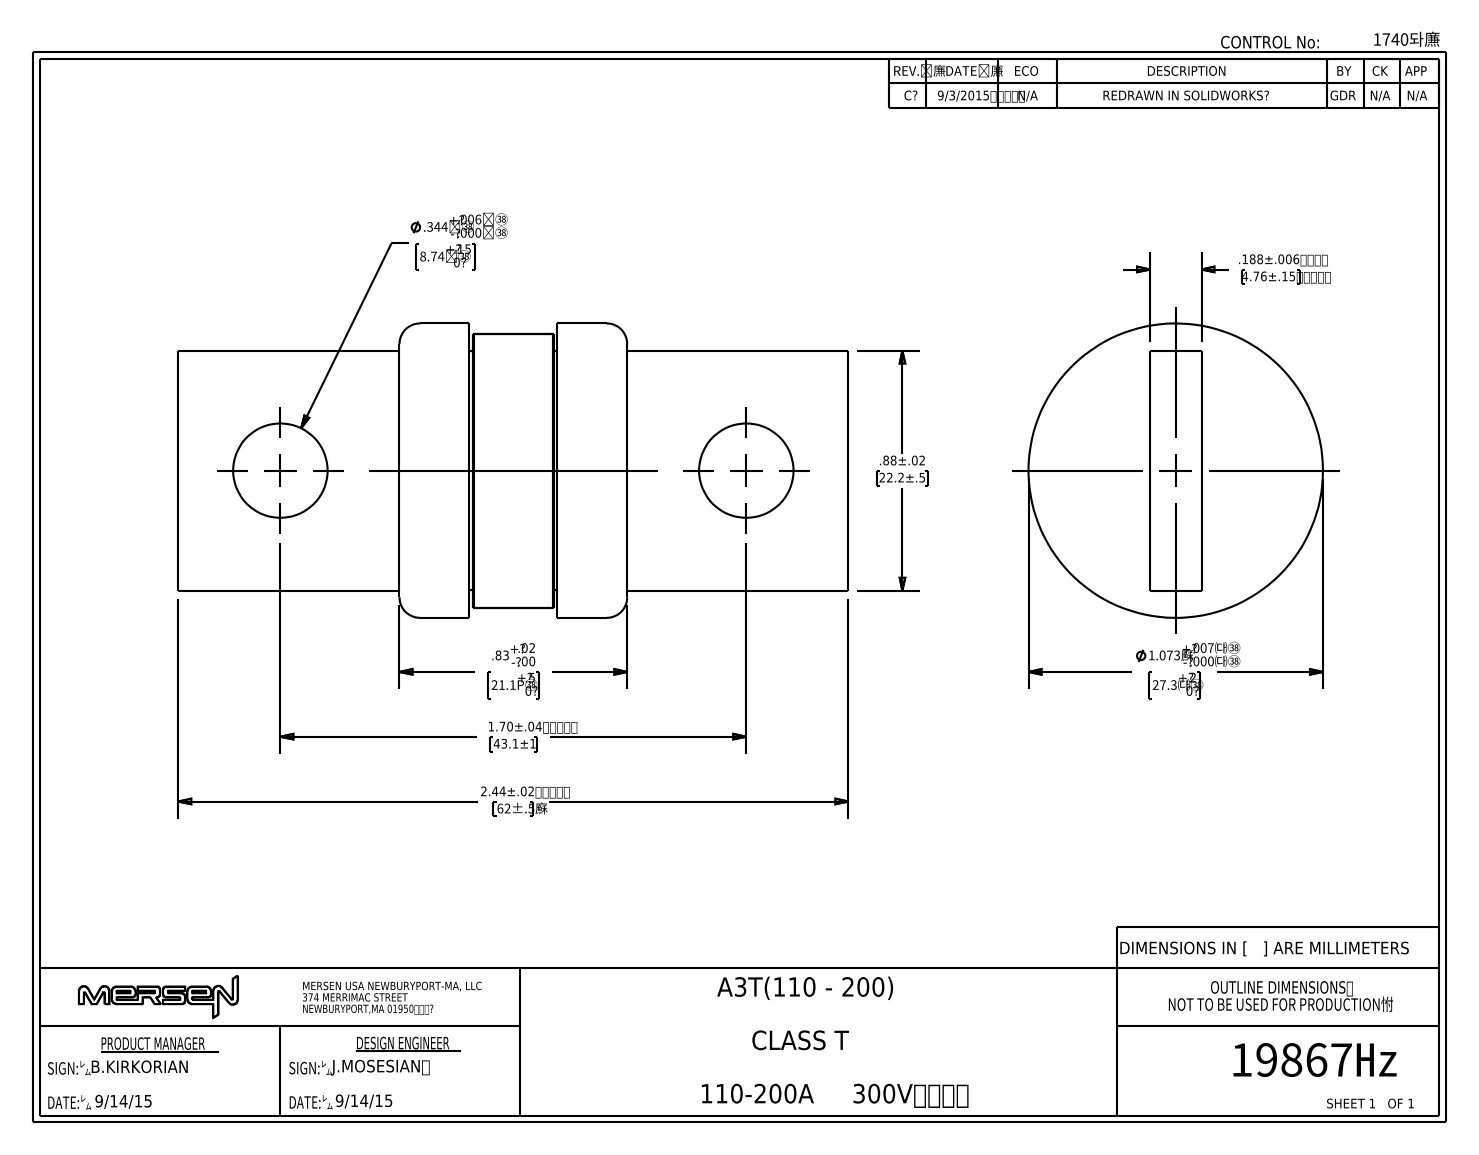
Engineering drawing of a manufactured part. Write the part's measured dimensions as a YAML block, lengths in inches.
part_name: "18832"
step_written_by: "SolidWorks 2014 (AUTOMOTIVE_DESIGN)"
units: inches
bodies: {solids: 0, faces: 36, planar: 14, cylindrical: 14, other: 8}
overall_size: [2.442, 1.073, 1.073]
round_holes:
  - {diameter: 0.344, count: 2}
round_bosses_or_shafts:
  - {diameter: 1.073, count: 1}
  - {diameter: 1, count: 1}
  - {diameter: 0.87, count: 1}
face_to_face_distances: [0.187, 0.83, 0.806, 1.636, 0.875, 0.561, 0.269, 0.27, 0.291, 0.56]
hole_center_spacings: [1.698]
